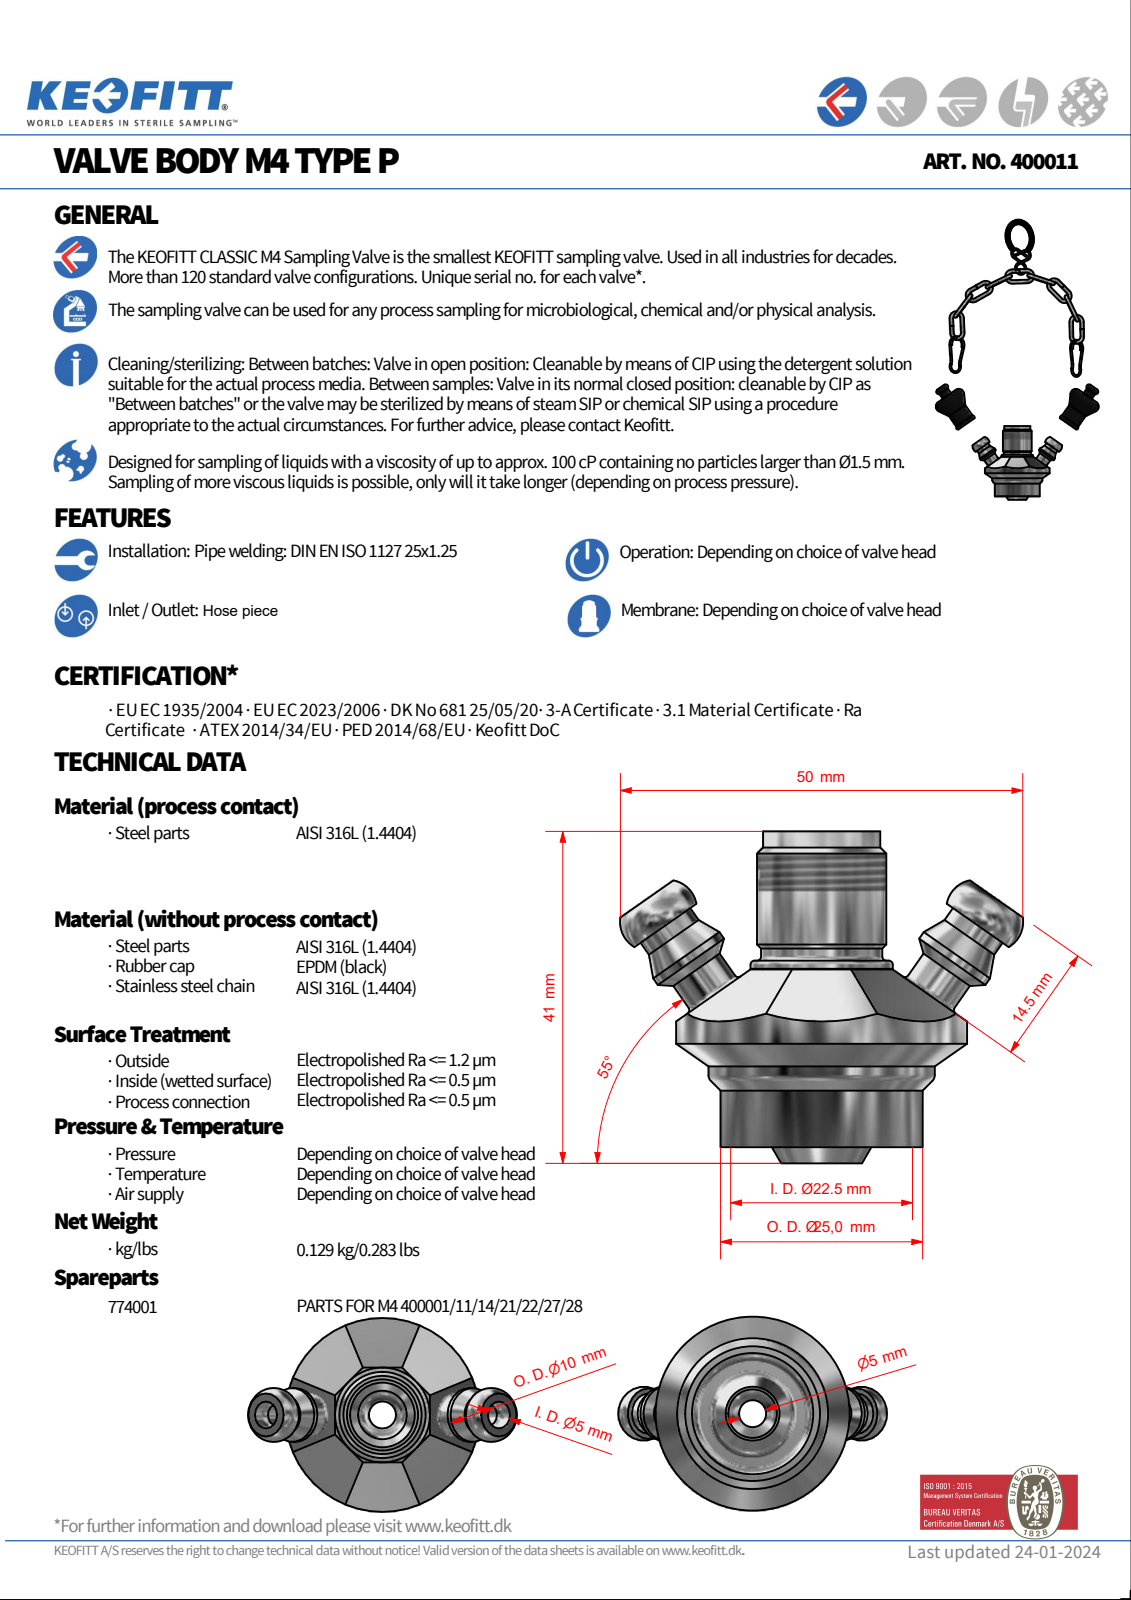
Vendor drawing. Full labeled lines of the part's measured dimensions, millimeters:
STEP written by: Autodesk Inventor 2008 (AUTOMOTIVE_DESIGN)
Units: millimetres
Bodies: 95 solids, 350 faces (96 planar, 82 cylindrical, 172 other)
Overall size (bounding box): 143.3 × 67.94 × 47.2
Volume: 25 589 mm³ · Surface area: 11 365 mm²
Round holes (diameter × count): ⌀2 ×9, ⌀3.5 ×2, ⌀5 ×1, ⌀13.2 ×1, ⌀22.5 ×1
Round bosses / shafts (diameter × count): ⌀2 ×21, ⌀11 ×2, ⌀10 ×2, ⌀7 ×2, ⌀6.5 ×2, ⌀5.6 ×2, ⌀5 ×2, ⌀4 ×2
Partial cylindrical surfaces — rounded edges, fillets, slot ends (radius × count): R0.1 ×9
Main face-to-face distances: 25.26, 1.18, 25, 23, 21.82, 18.26, 7, 2, 22, 20.82
